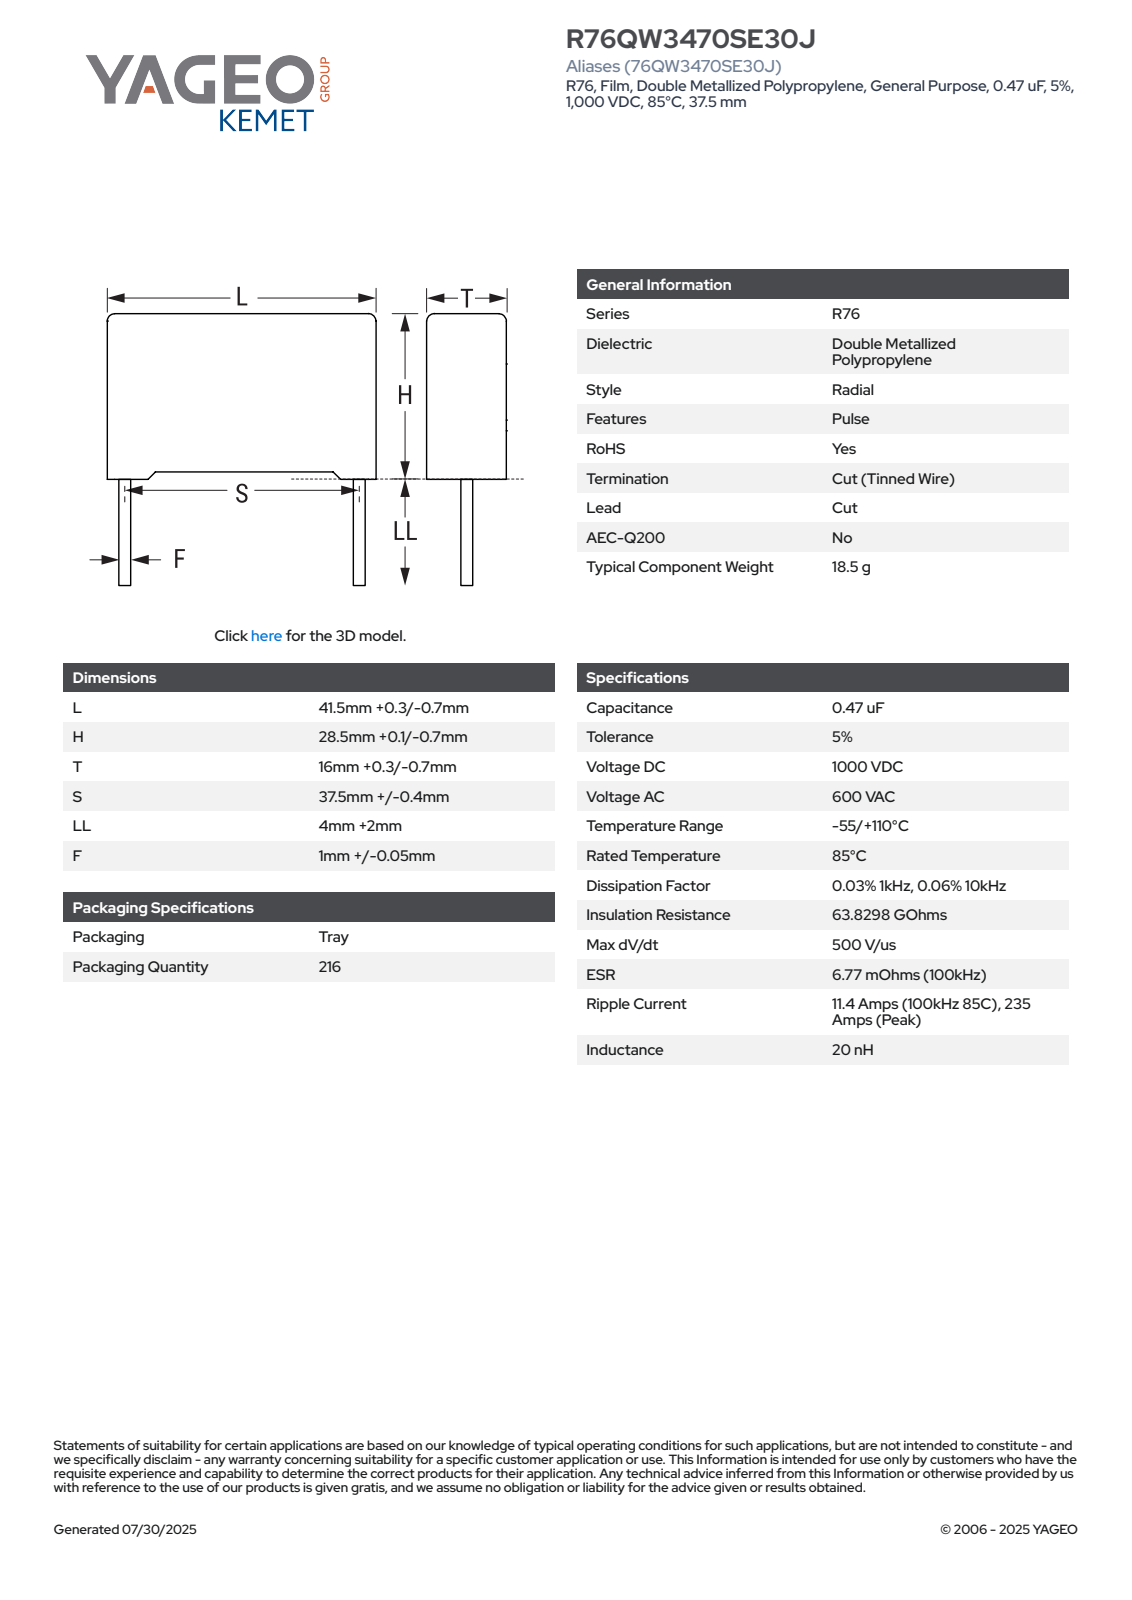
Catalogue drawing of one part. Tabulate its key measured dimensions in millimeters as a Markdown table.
| quantity | value |
| --- | --- |
| part name | CFR_RB2_41.5X28.5X16_L41.8H28.6T16.3S37.5LL6F1.05 |
| STEP written by | SolidWorks 2021 (AUTOMOTIVE_DESIGN) |
| units | millimeters |
| bodies | 4 solids, 85 faces (77 planar, 8 cylindrical, 0 other) |
| overall size | 41.8 × 34.6 × 16.3 |
| volume | 18 902 mm³ |
| surface area | 4 803 mm² |
| round bosses / shafts (diameter × count) | 1.05 × 2 |
| partial cylindrical surfaces (radius × count) | 0.5 × 4 |
| main face-to-face distances | 16.3, 27.61, 41.8, 27.85, 0.75, 0.99, 28.6, 16.31, 1.39, 40.41 |
